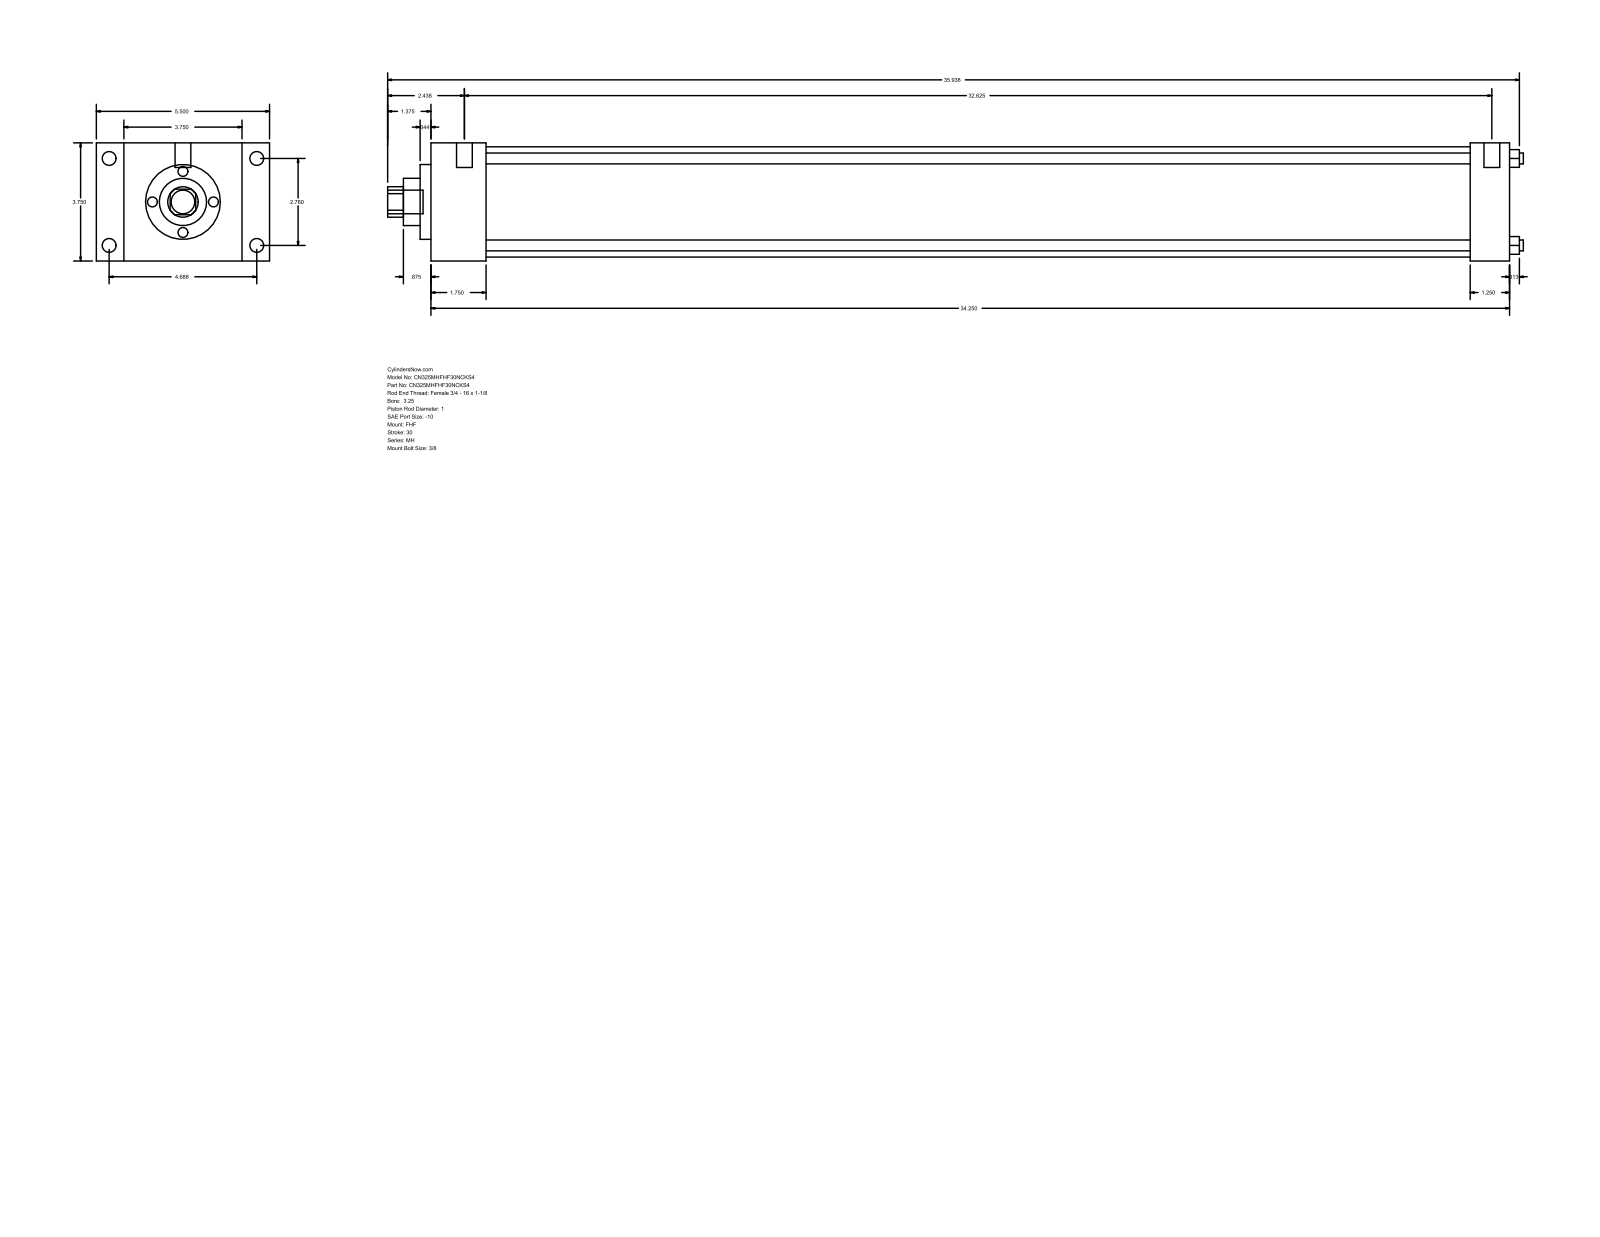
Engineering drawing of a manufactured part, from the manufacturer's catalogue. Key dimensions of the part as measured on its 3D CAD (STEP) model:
Part name (STEP PRODUCT): MH_FHF__0325_1
STEP written by: GSSL Pune (CONFIG_CONTROL_DESIGN)
Units: millimetres
Bodies: 0 solids, 90 faces (61 planar, 29 cylindrical, 0 other)
Overall size (bounding box): 915.99 × 139.7 × 95.25
Round holes (diameter × count): ⌀8.76 ×4, ⌀25.4 ×1, ⌀38.1 ×1, ⌀60.33 ×1, ⌀88.9 ×1
Round bosses / shafts (diameter × count): ⌀11.13 ×4, ⌀5.56 ×4, ⌀12.7 ×2, ⌀19.05 ×1
Partial cylindrical surfaces — rounded edges, fillets, slot ends (radius × count): R12.29 ×1
Main face-to-face distances: 95.24, 869.96, 44.46, 825.5, 22.23, 117.47, 139.7, 838.2, 793.74, 31.76
Hole centre spacings: 49.57, 70.1, 99.14
